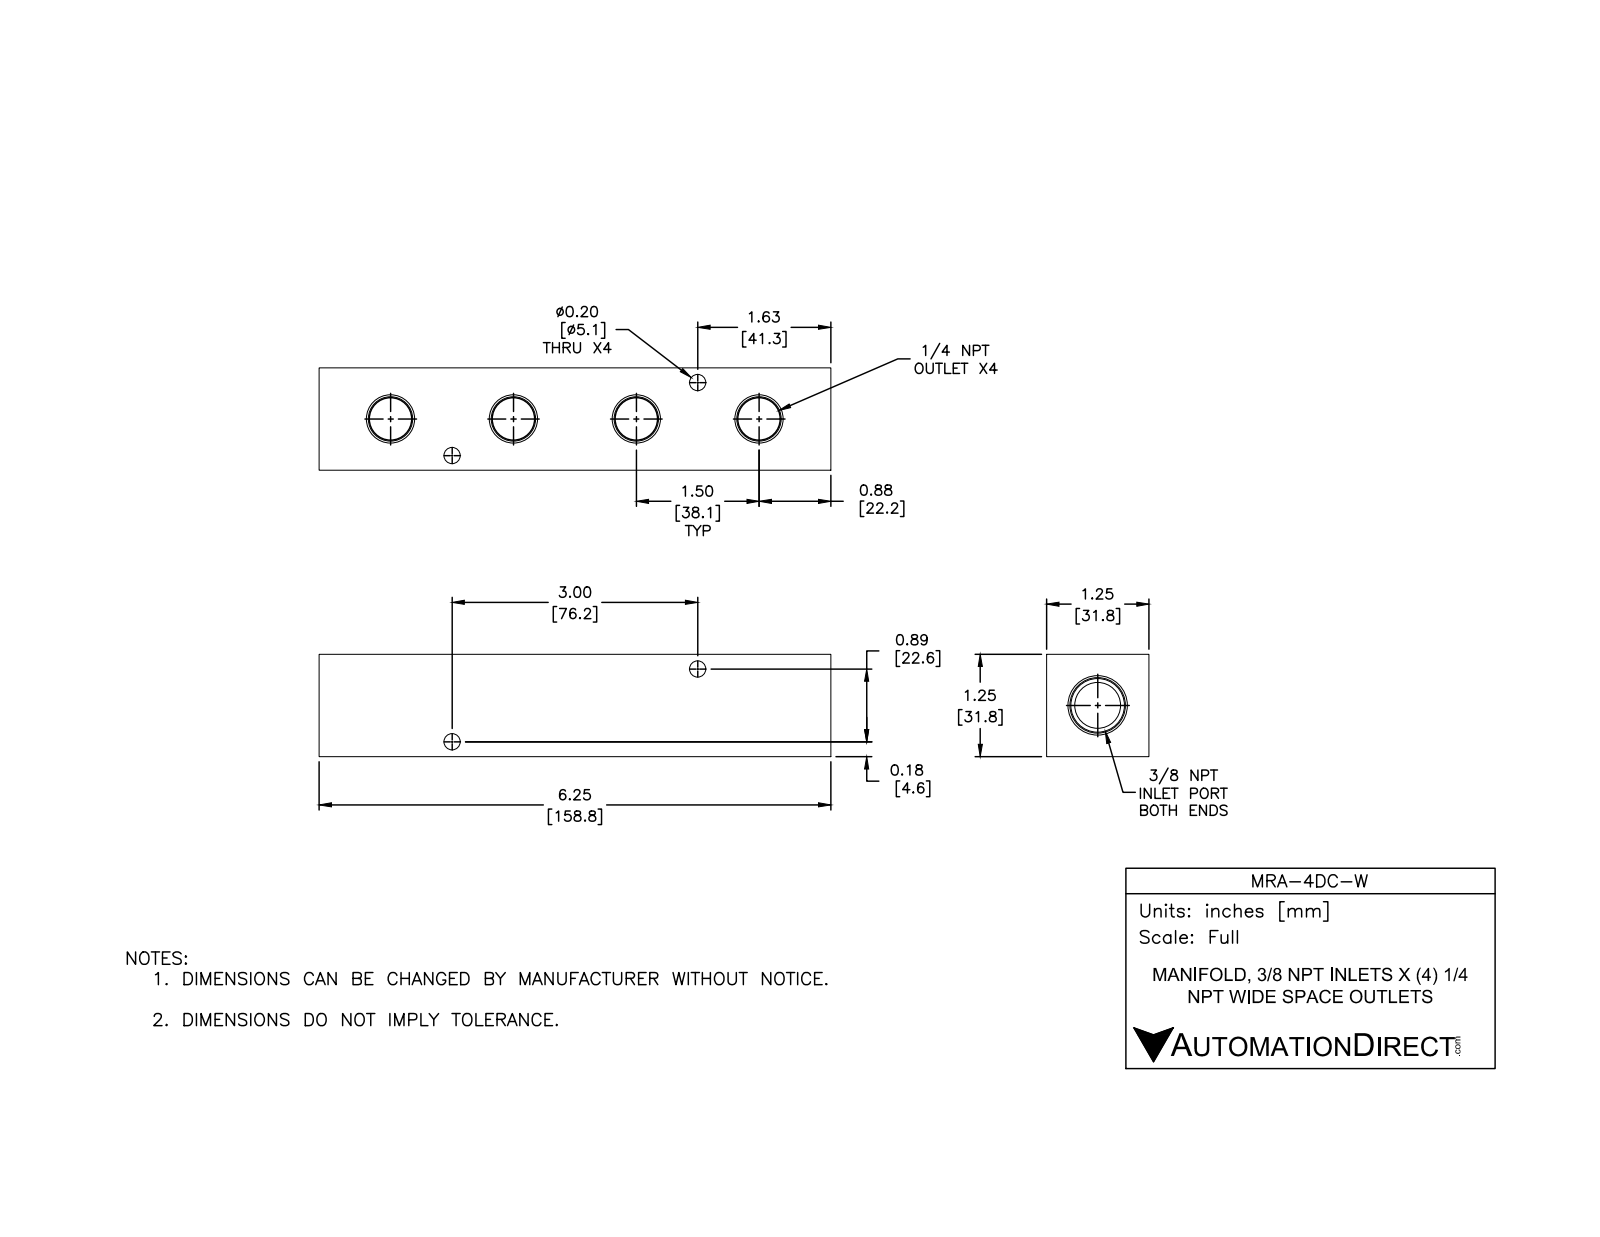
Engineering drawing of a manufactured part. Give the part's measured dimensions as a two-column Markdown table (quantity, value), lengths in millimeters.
| quantity | value |
| --- | --- |
| part name | MRA-4DC-W |
| STEP written by | SolidWorks 2015 (CONFIG_CONTROL_DESIGN) |
| units | millimeters |
| bodies | 1 solid, 66 faces (16 planar, 26 cylindrical, 24 other) |
| overall size | 158.8 × 31.8 × 31.8 |
| volume | 125 500 mm³ |
| surface area | 31 350 mm² |
| round holes (diameter × count) | 5.1 × 4, 14.3 × 1 |
| partial cylindrical surfaces (radius × count) | 5.6 × 4 |
| main face-to-face distances | 31.8, 158.8, 10.4, 148.3, 21.8, 9.9, 137.9 |
| hole center spacings | 79.5 |
